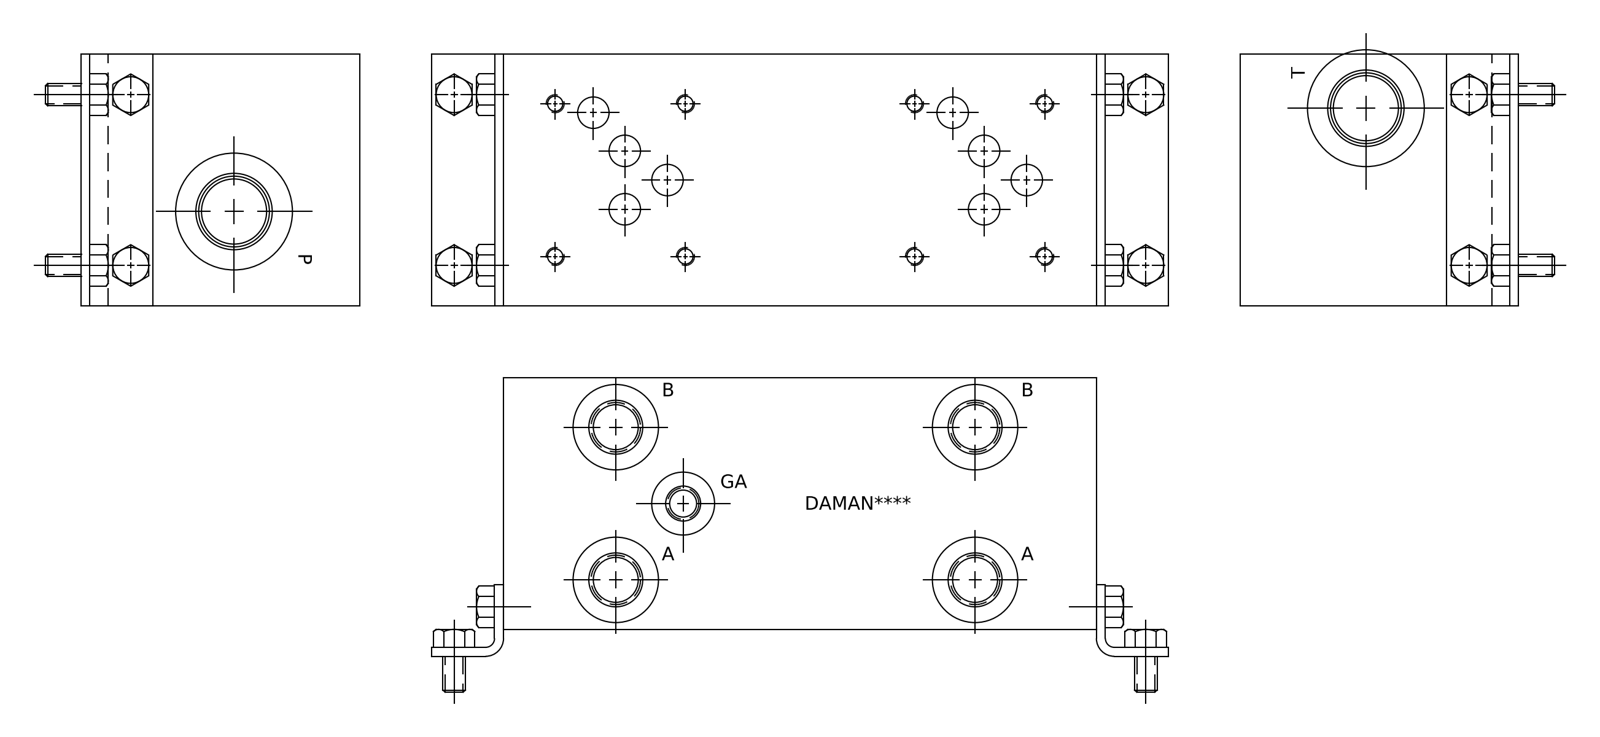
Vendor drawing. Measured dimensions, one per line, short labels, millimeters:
name: Part_AD05S025S.C02249R4_3D
written by: Autodesk Inventor 2020 (AUTOMOTIVE_DESIGN)
unit: mm
bodies: 1 solid, 599 faces (323 planar, 68 cylindrical, 208 other)
size: 209.55 × 88.9 × 88.9
volume: 1 579 000 mm³; area: 107 586 mm²
holes: 9× ⌀11.13, 8× ⌀5.11, 8× ⌀6.35, 4× ⌀15.88, 4× ⌀17.5, 4× ⌀19.05, 4× ⌀19.25, 4× ⌀30.63, 2× ⌀6.53, 2× ⌀7.92, 2× ⌀23.01, 2× ⌀24.92
face distances: 88.9, 209.55, 0.79, 88.11, 208.76, 207.97, 19.05, 0.75, 88.86, 15.06
hole spacings: 127, 137.99, 53.97, 46.05, 70.95, 13.88, 18.27, 27.73
